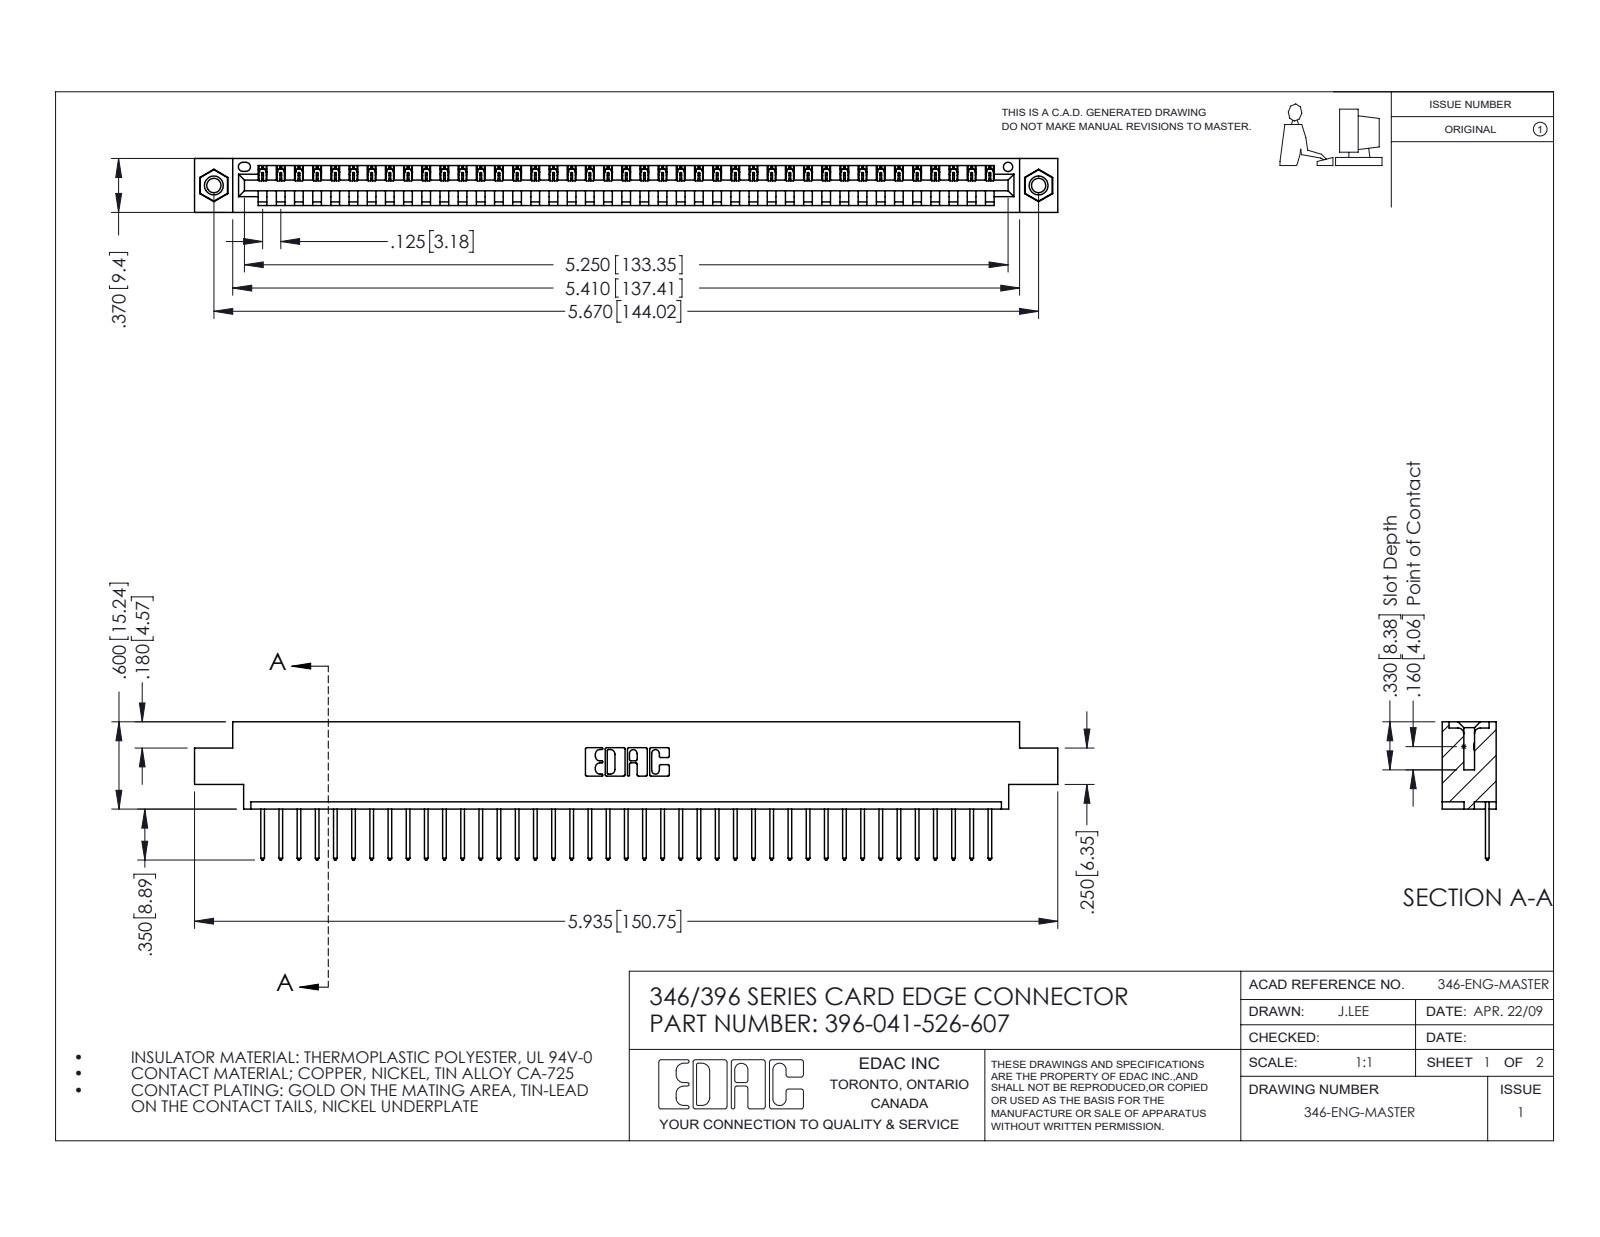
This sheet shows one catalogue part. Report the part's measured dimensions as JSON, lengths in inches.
{"part_name": "345-250-001_345-250-005-103; 346 Part_0.170 Offset - 0.156 Dia-TI; 345-292-001_345-293-126; 396-041-526-607", "step_written_by": "SolidWorks 2016 (CONFIG_CONTROL_DESIGN)", "units": "inches", "bodies": {"solids": 44, "faces": 2564, "planar": 1752, "cylindrical": 796, "other": 16}, "overall_size": [5.935, 0.95, 0.37], "volume_in3": 0.868, "surface_area_in2": 27.78, "round_holes": [[0.098, 2], [0.125, 2], [0.156, 2], [0.064, 1]], "round_bosses_or_shafts": [[0.155, 2]], "partial_cylinders_radius": [[0.006, 82], [0.01, 82], [0.01, 22], [0.007, 6], [0.031, 6], [0.026, 3], [0.031, 2], [0.04, 2]], "face_to_face_distances": [0.048, 0.322, 0.37, 0.25, 0.072, 0.298, 0.025, 0.222, 0.148, 0.1], "hole_center_spacings": [0.246, 5.461, 5.67]}
